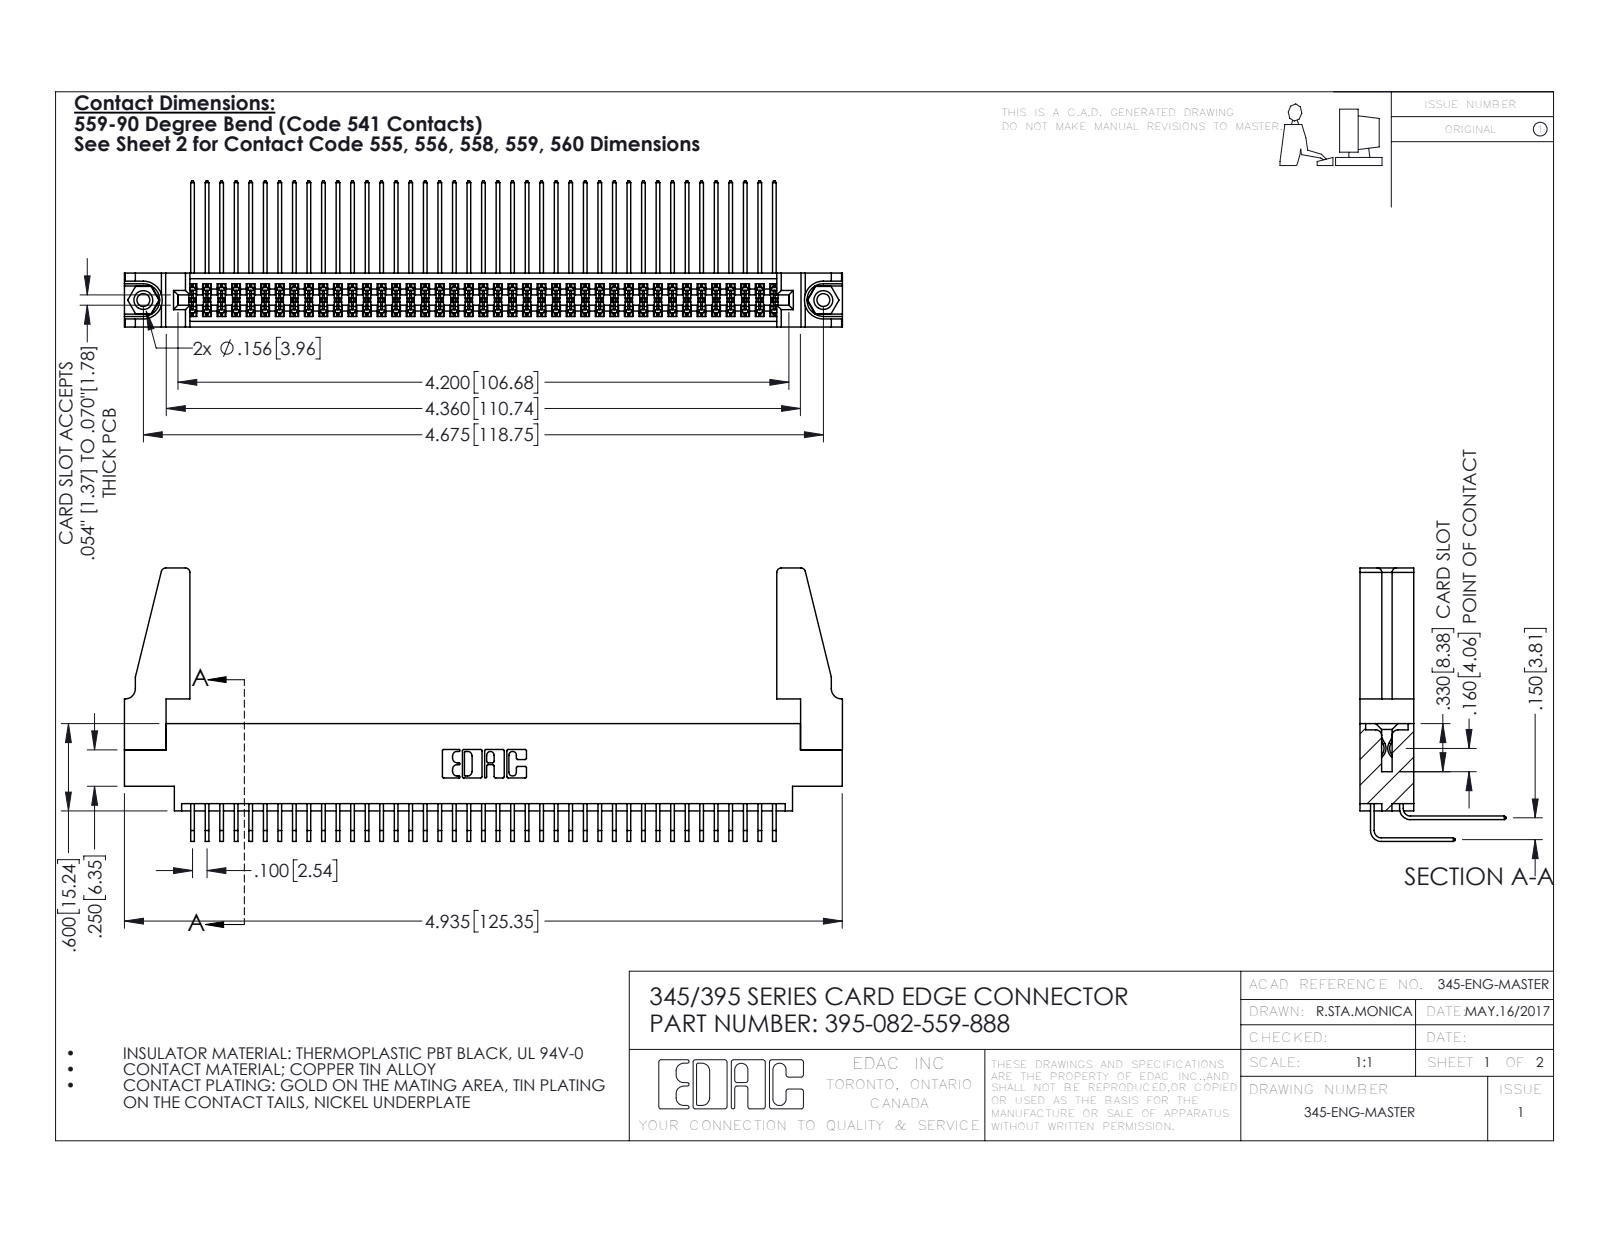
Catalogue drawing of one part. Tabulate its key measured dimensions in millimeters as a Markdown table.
| quantity | value |
| --- | --- |
| part name | 395-082-559-888; 345-292-001_559 Tail - 2; 345-292-001_558 559 Tail - 1; 345-250-001_345-250-001-102 (+2 more) |
| STEP written by | SolidWorks 2016 (CONFIG_CONTROL_DESIGN) |
| units | millimeters |
| bodies | 87 solids, 4518 faces (3026 planar, 1476 cylindrical, 16 other) |
| overall size | 125.4 × 47.7 × 25.5 |
| volume | 15 800 mm³ |
| surface area | 23 990 mm² |
| round holes (diameter × count) | 2.3 × 2, 3.2 × 2, 4 × 2, 1.6 × 1 |
| round bosses / shafts (diameter × count) | 3.9 × 2 |
| partial cylindrical surfaces (radius × count) | 0.2 × 123, 0.3 × 22, 0.8 × 8, 0.2 × 6, 0.8 × 6, 0.7 × 3, 0.4 × 2, 0.5 × 2 |
| main face-to-face distances | 1.8, 7.6, 9.4, 5.1, 2.5, 6.9, 0.6, 5.7, 3.8, 4.4 |
| hole center spacings | 6.9, 112.8, 118.7 |
